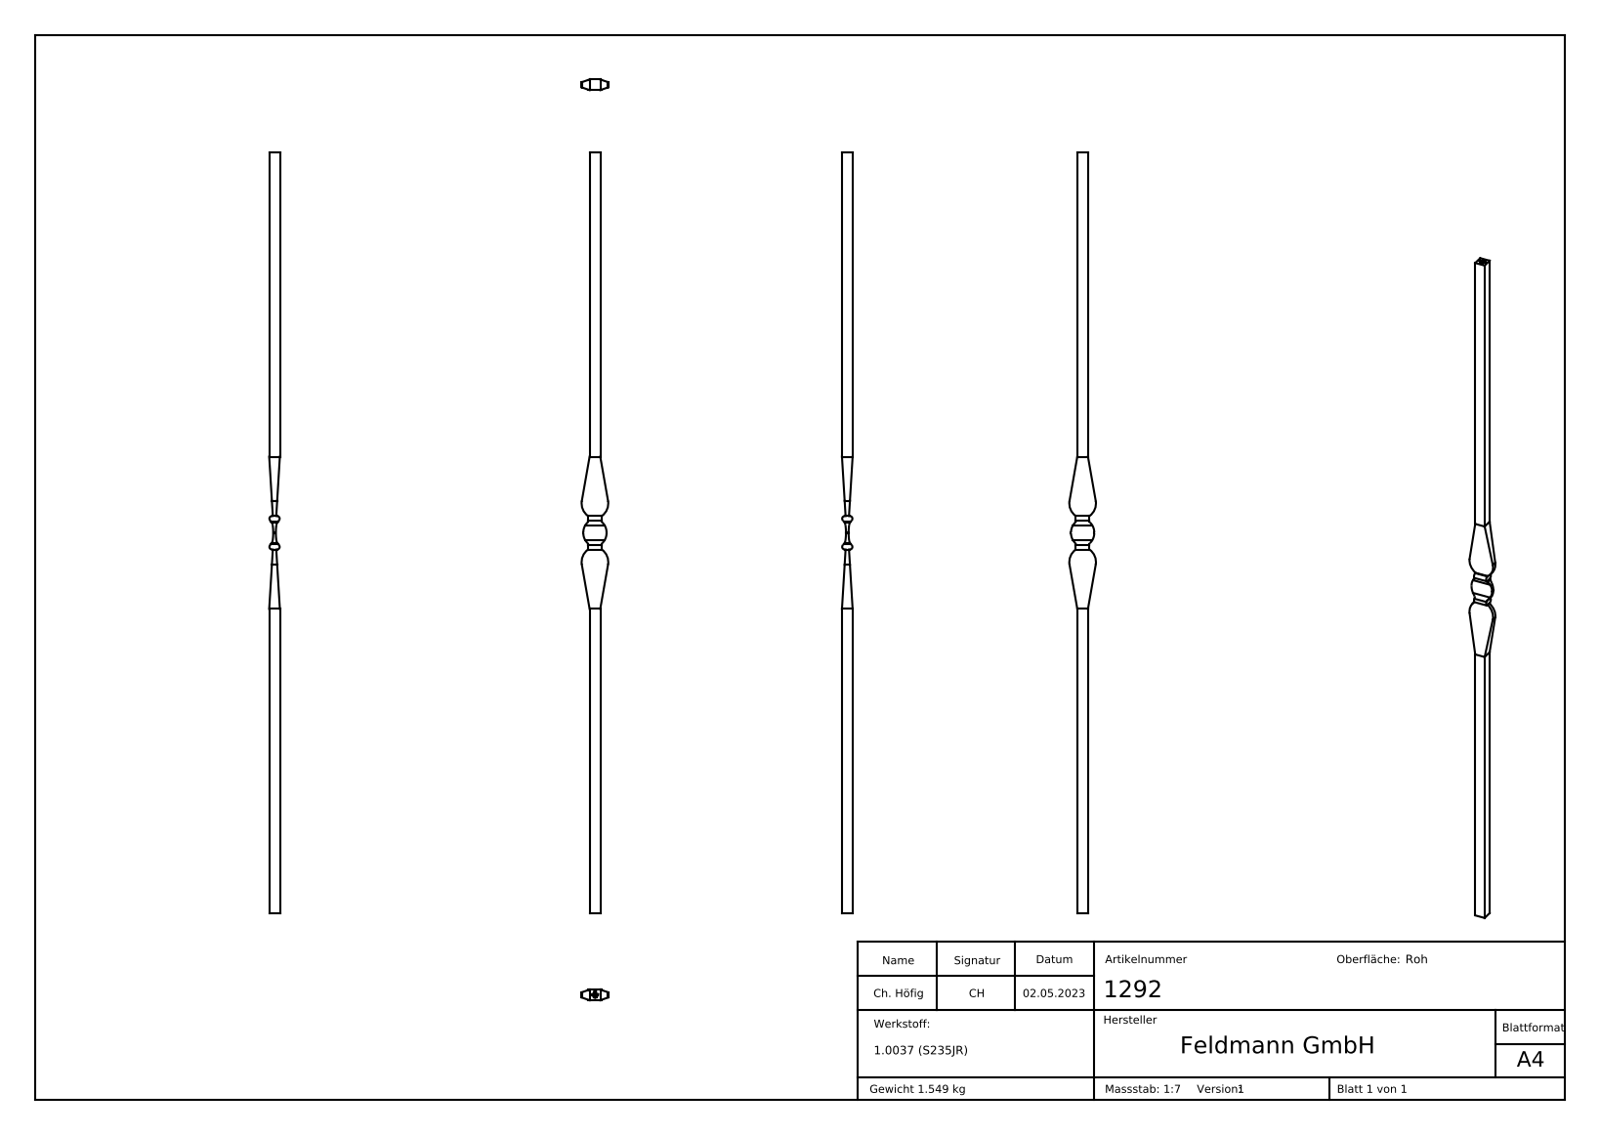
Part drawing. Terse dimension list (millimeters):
name: 1292
written by: SolidWorks 2018 (CONFIG_CONTROL_DESIGN)
unit: mm
bodies: 1 solid, 253 faces (142 planar, 22 cylindrical, 89 other)
size: 1000 × 35 × 14
volume: 198 613 mm³; area: 59 333 mm²
rounds: 4× R1.95, 4× R3.5, 4× R10, 4× R18, 4× R20.25, 2× R75.75
face distances: 14, 1.78, 48.38, 2, 16, 1000, 18, 478, 522, 44
